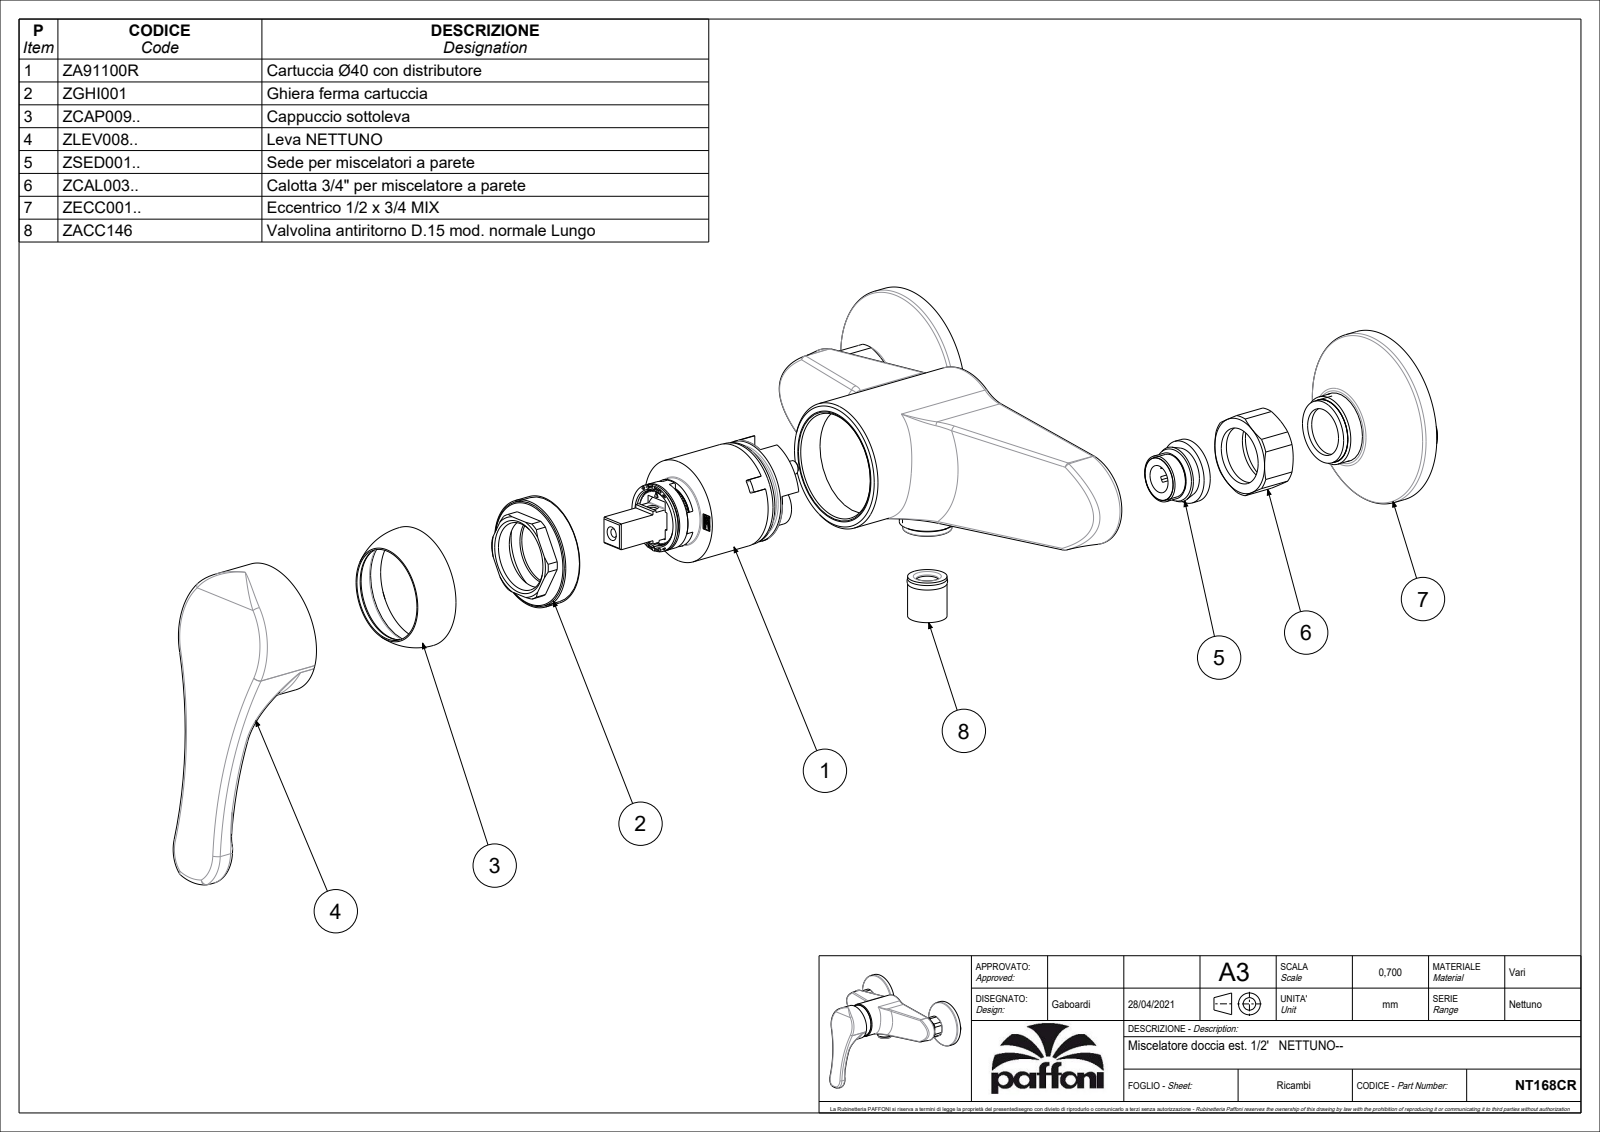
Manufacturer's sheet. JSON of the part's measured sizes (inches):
{"part_name": "NT168CR", "step_written_by": "CREO PARAMETRIC BY PTC INC, 2020044 (CONFIG_CONTROL_DESIGN)", "units": "inches", "bodies": {"solids": 3, "faces": 1411, "planar": 631, "cylindrical": 400, "other": 380}, "overall_size": [8.484, 5.915, 4.705], "volume_in3": 12.03, "surface_area_in2": 199.4, "round_holes": [[0.315, 4], [0.276, 2], [0.413, 2], [0.472, 2], [0.591, 2], [0.65, 2], [0.709, 2], [0.846, 2], [0.949, 2], [1.051, 2], [2.5, 2], [0.13, 1]], "round_bosses_or_shafts": [[2.579, 2], [1.115, 2], [0.945, 2], [0.626, 2], [0.37, 2], [1.969, 1], [1.909, 1], [1.555, 1]], "partial_cylinders_radius": [[0.02, 51], [0.008, 24], [0.039, 5], [0.079, 5], [0.012, 4], [0.059, 4], [0.61, 3], [0.217, 2]], "face_to_face_distances": [0.138, 0.295, 0.433, 0.256, 0.197, 0.039, 0.394, 0.492, 0.551, 0.059], "hole_center_spacings": [0.39, 0.079, 0.339, 0.347, 0.4, 0.513, 0.551, 0.557]}
